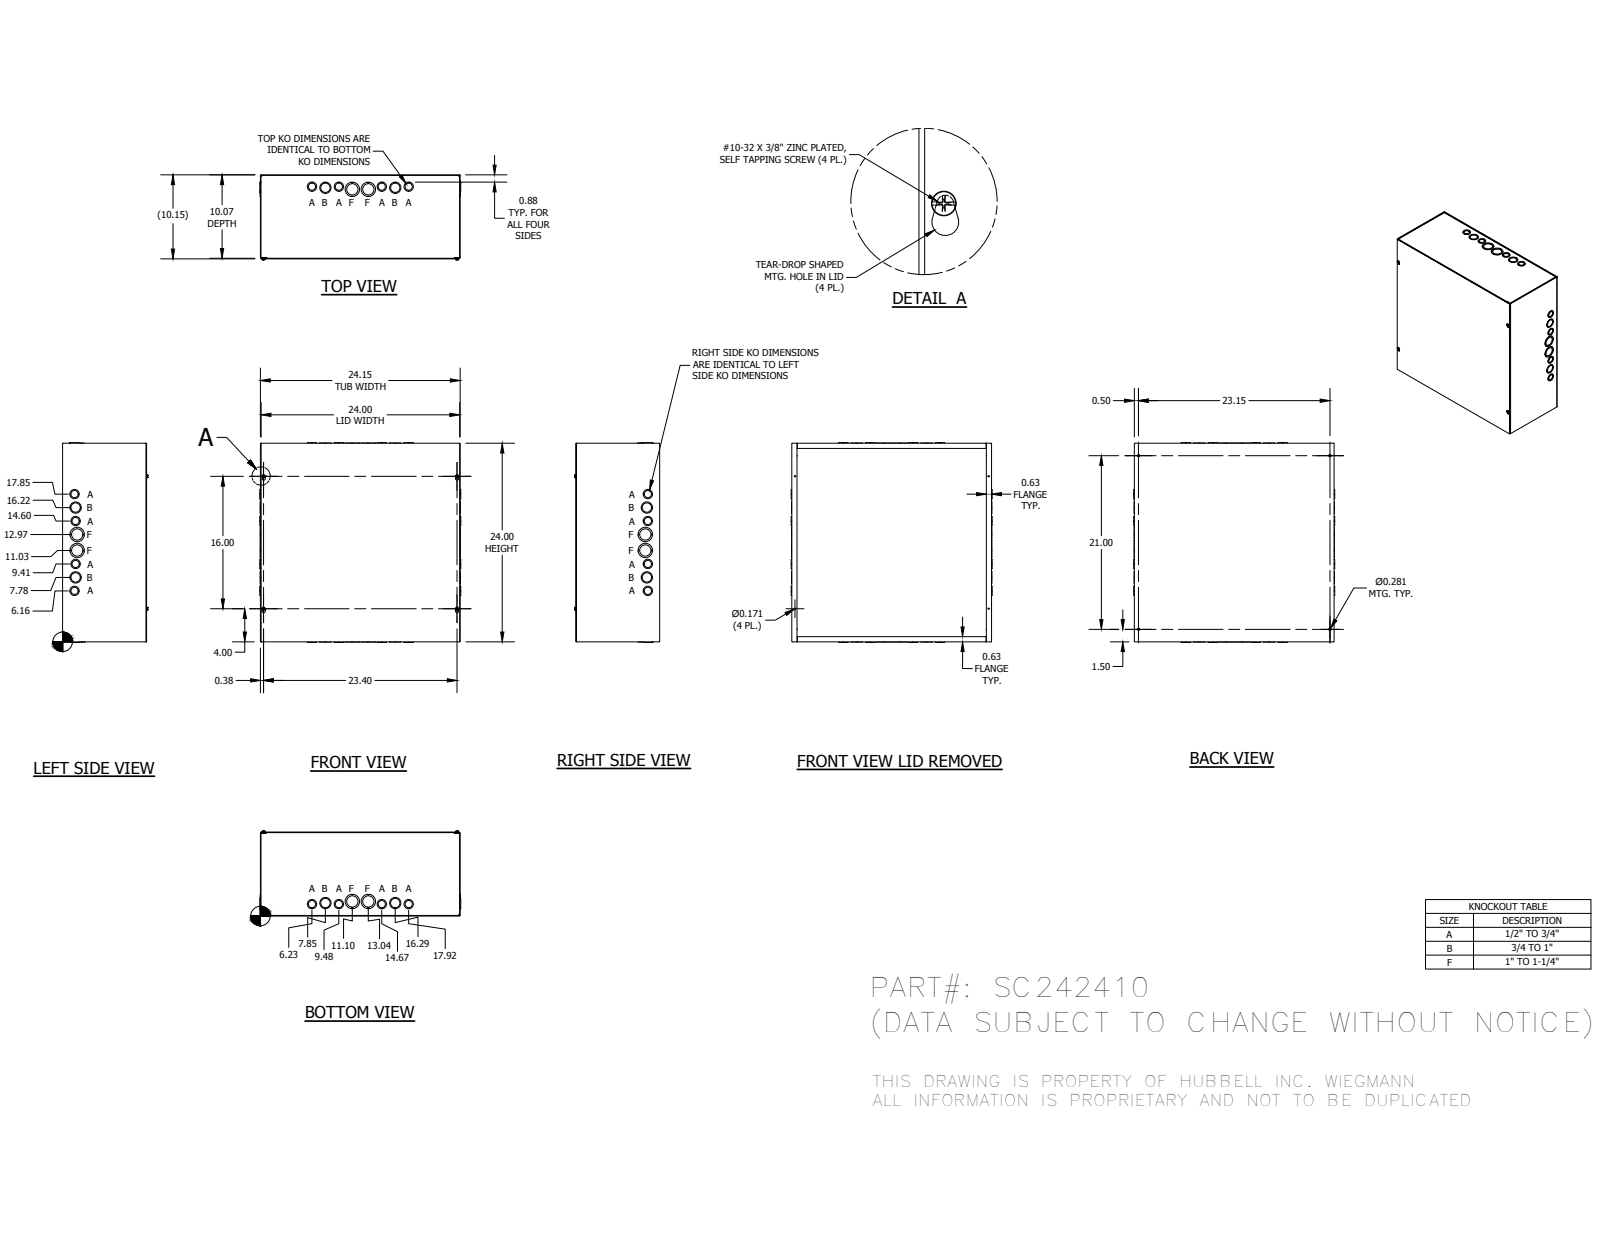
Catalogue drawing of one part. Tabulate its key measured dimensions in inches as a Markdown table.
| quantity | value |
| --- | --- |
| part name | SC242410BLR; SC2410TB; SC2424LPA; 37214 (+1 more) |
| STEP written by | Autodesk Inventor 2014 (AUTOMOTIVE_DESIGN) |
| units | inches |
| bodies | 37 solids, 1219 faces (899 planar, 236 cylindrical, 84 other) |
| overall size | 24.296 × 24.148 × 10.28 |
| round holes (diameter × count) | 1.125 × 14, 0.875 × 10, 1.375 × 8, 0.171 × 4, 0.281 × 4, 1.75 × 4 |
| round bosses / shafts (diameter × count) | 0.19 × 4 |
| partial cylindrical surfaces (radius × count) | 0.016 × 12, 0.09 × 12, 0.125 × 4, 0.203 × 4 |
| main face-to-face distances | 0.074, 10.074, 10, 10.148, 24, 23.926, 24.074, 24.148, 23.852, 0.148 |
| hole center spacings | 1.63, 1.63, 1.655, 2.503, 3.25, 3.256, 3.579, 4.885 |
